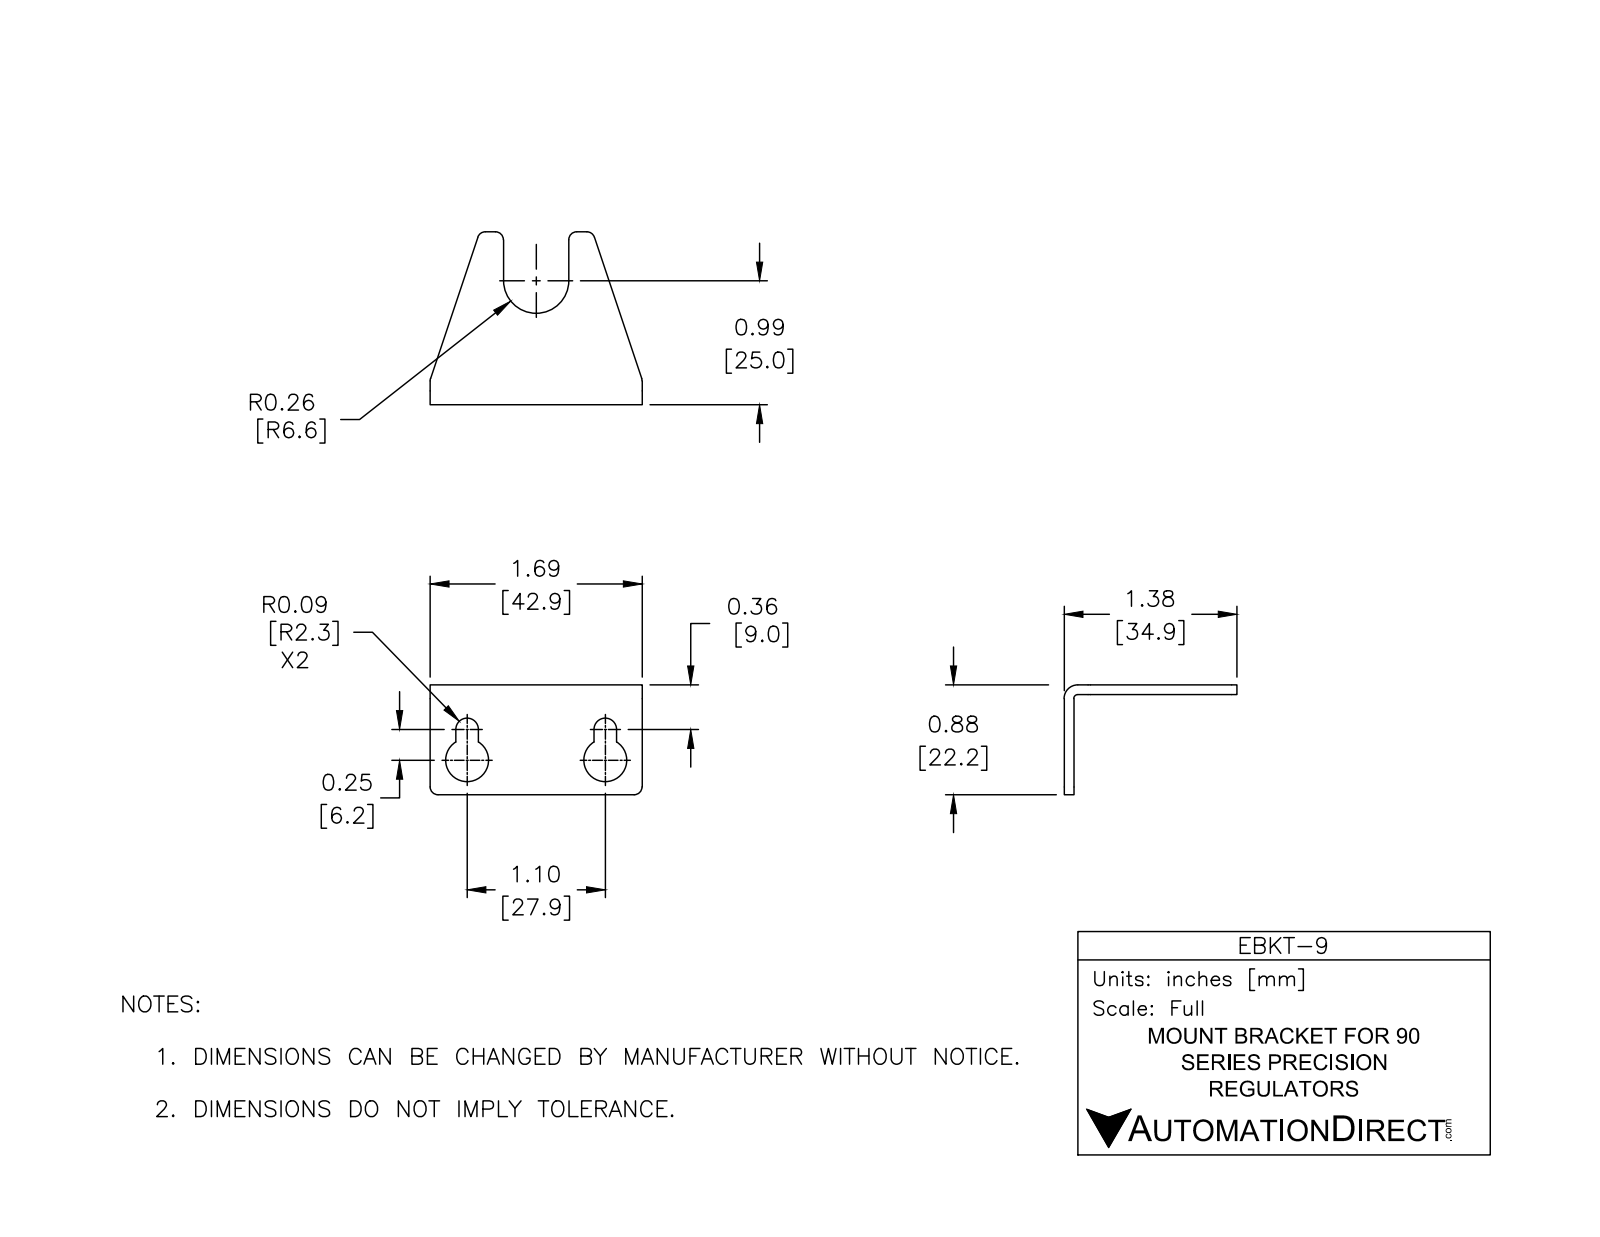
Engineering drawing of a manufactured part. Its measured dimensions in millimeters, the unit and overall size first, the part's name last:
Units: millimetres
Overall size (bounding box): 42.86 × 34.92 × 22.23
Round holes (diameter × count): ⌀8.64 ×2
Partial cylindrical surfaces — rounded edges, fillets, slot ends (radius × count): R1.6 ×8, R2.29 ×2, R0.8 ×1, R2.78 ×1, R6.6 ×1
Main face-to-face distances: 1.98, 20.24, 22.22, 42.86, 14.83, 28.03, 13.2, 5.17, 9.75, 33.11
Hole centre spacings: 27.94
Volume: 3 325 mm³ · Surface area: 3 893 mm²
Bodies: 1 solid, 32 faces (17 planar, 15 cylindrical, 0 other)
Part name (STEP PRODUCT): 707075
STEP written by: Autodesk Inventor 2014 (AUTOMOTIVE_DESIGN)
